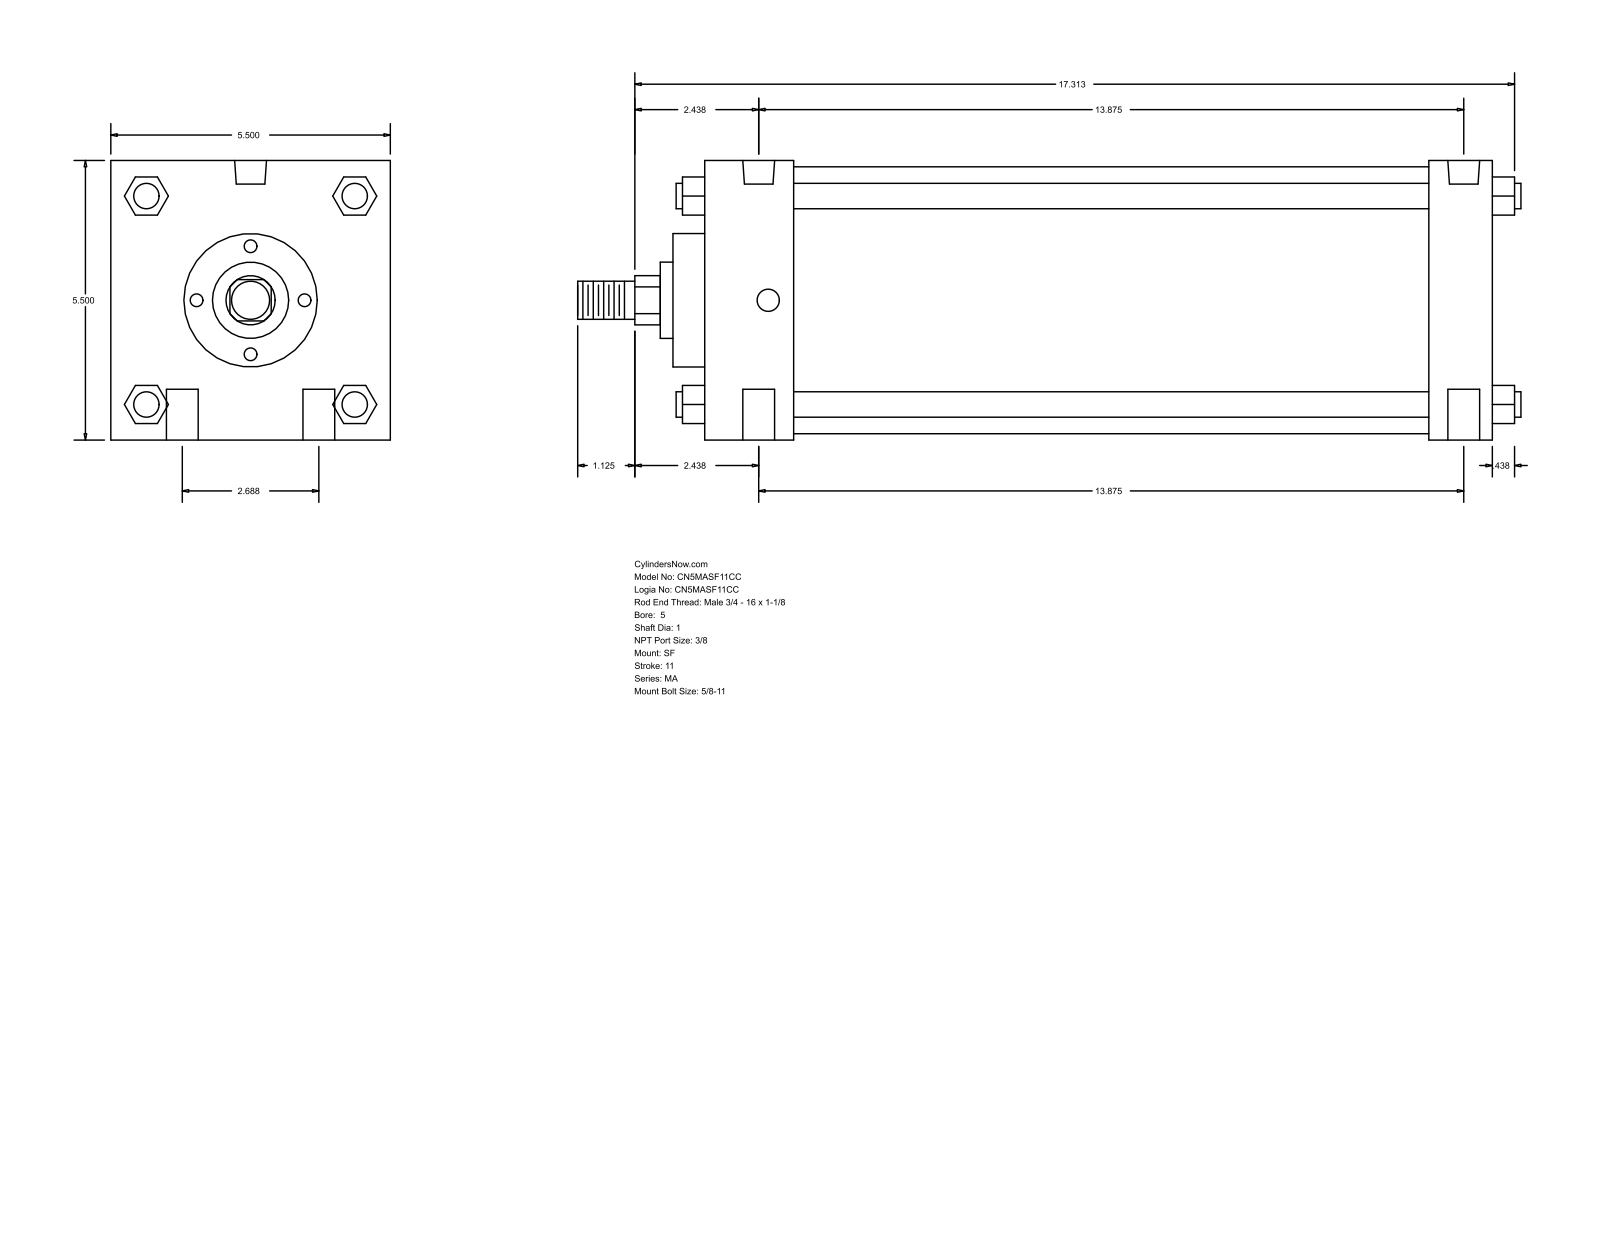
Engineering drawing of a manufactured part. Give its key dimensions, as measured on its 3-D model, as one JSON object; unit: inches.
{"part_name": "MA_SF__0500_1", "step_written_by": "GSSL Pune (CONFIG_CONTROL_DESIGN)", "units": "inches", "bodies": {"solids": 0, "faces": 126, "planar": 95, "cylindrical": 31, "other": 0}, "overall_size": [18.563, 5.5, 5.5], "round_holes": [[0.625, 4], [0.437, 2], [0.627, 2]], "round_bosses_or_shafts": [[0.5, 4], [5.25, 1], [2.625, 1], [1.5, 1], [1, 1], [0.75, 1]], "partial_cylinders_radius": [[0.484, 1]], "face_to_face_distances": [5.5, 15.5, 1.75, 14.25, 12.5, 13.75, 1.25, 0.625, 2.375, 14.875], "hole_center_spacings": [1.344, 13.94, 13.875, 2.687, 14.133, 13.5]}
